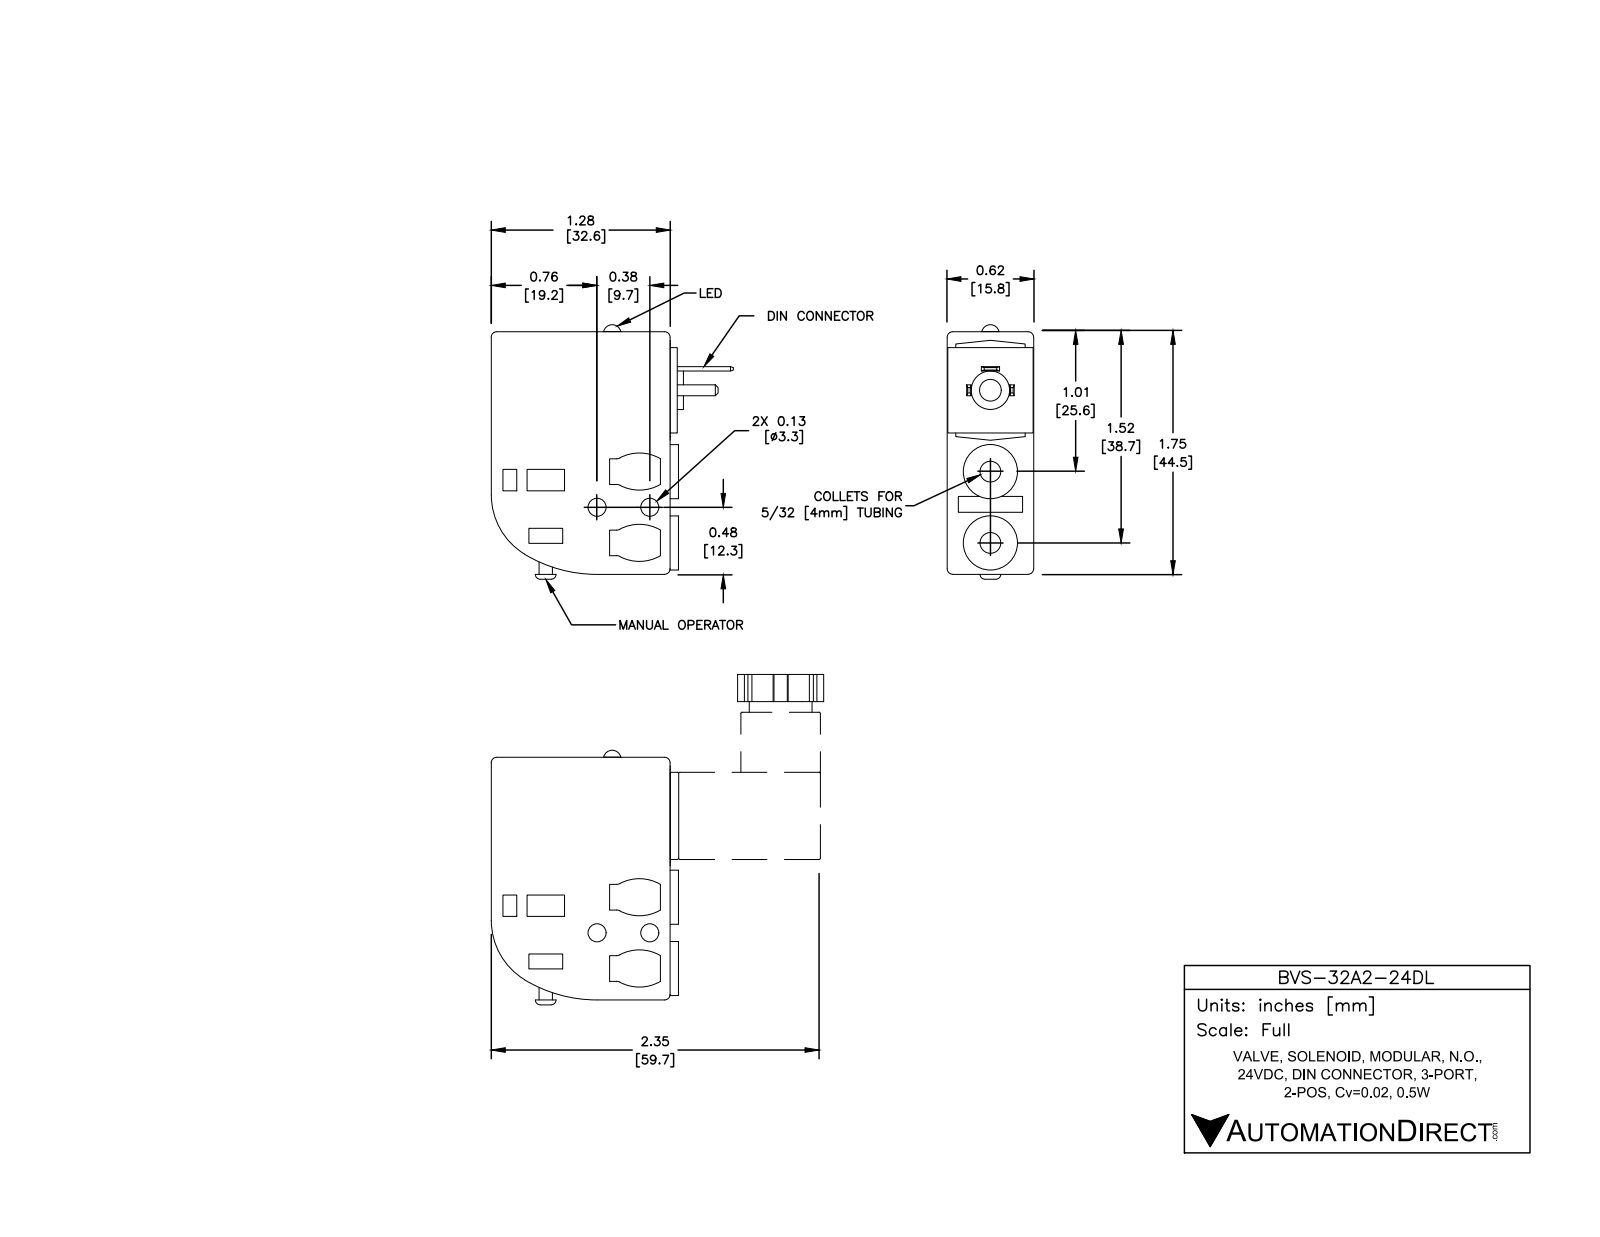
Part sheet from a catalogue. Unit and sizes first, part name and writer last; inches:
Units: inches
Overall size (bounding box): 1.84 × 1.75 × 0.62
Round holes (diameter × count): ⌀0.13 ×2, ⌀0.15 ×2, ⌀0.25 ×2, ⌀0.05 ×1, ⌀0.16 ×1
Round bosses / shafts (diameter × count): ⌀0.39 ×2, ⌀0.28 ×1, ⌀0.1 ×1
Partial cylindrical surfaces — rounded edges, fillets, slot ends (radius × count): R0.05 ×4, R0.3 ×4, R0.04 ×3, R0.5 ×1, R1 ×1
Main face-to-face distances: 0.62, 0.1, 1.29, 0.52, 1.341, 0.051, 1.75, 1, 0.15, 0.06
Hole centre spacings: 0.06, 0.38, 0.45, 0.51, 0.59, 0.65, 1.1
Volume: 1.279 in³ · Surface area: 10.75 in²
Bodies: 1 solid, 162 faces (112 planar, 46 cylindrical, 4 other)
Part name (STEP PRODUCT): BVS-32A2-24DL
STEP written by: SolidWorks 2016 (AUTOMOTIVE_DESIGN)
